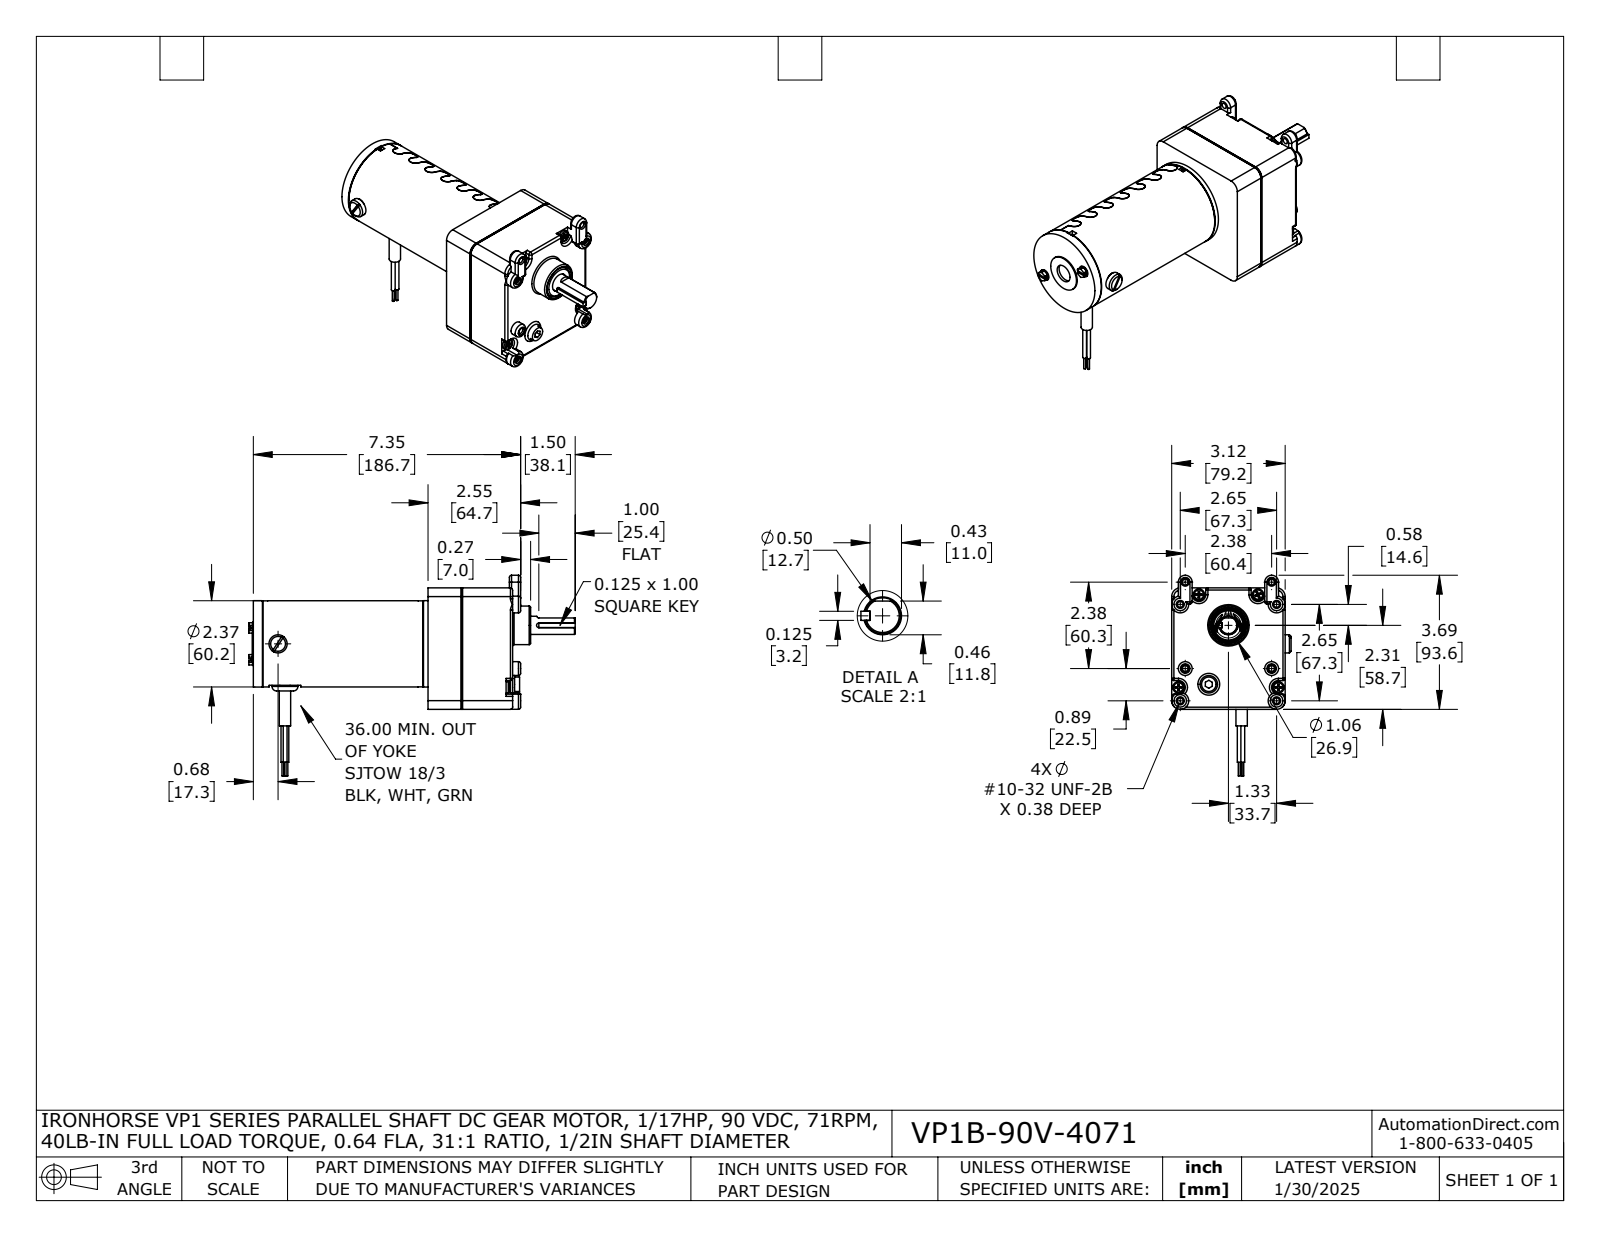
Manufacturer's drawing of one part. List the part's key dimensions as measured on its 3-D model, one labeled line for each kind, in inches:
Part name (STEP PRODUCT): VP1B-90V-4071
STEP written by: SolidWorks 2021 (AUTOMOTIVE_DESIGN)
Units: inches
Bodies: 20 solids, 916 faces (340 planar, 422 cylindrical, 154 other)
Overall size (bounding box): 8.974 × 5.516 × 3.283
Volume: 12.28 in³ · Surface area: 225.5 in²
Round holes (diameter × count): ⌀0.2 ×11, ⌀0.158 ×8, ⌀0.18 ×4, ⌀0.187 ×2, ⌀0.189 ×2, ⌀0.22 ×2, ⌀0.213 ×1, ⌀0.336 ×1, ⌀0.468 ×1, ⌀0.5 ×1, ⌀0.521 ×1, ⌀0.688 ×1
Round bosses / shafts (diameter × count): ⌀0.314 ×4, ⌀0.313 ×4, ⌀0.136 ×4, ⌀0.105 ×3, ⌀0.052 ×3, ⌀0.5 ×2, ⌀0.466 ×2, ⌀0.44 ×2
Partial cylindrical surfaces — rounded edges, fillets, slot ends (radius × count): R0.06 ×34, R0.062 ×21, R0.156 ×14, R0.151 ×7, R0.161 ×7, R0.15 ×6, R0.12 ×4, R0.235 ×4
Main face-to-face distances: 0.09, 3.12, 1.38, 2.326, 0.946, 0.106, 1.274, 2.22, 3.34, 0.315
Hole centre spacings: 1.68, 2.65, 1.074, 2.729, 3.093, 0.077, 0.297, 0.373
